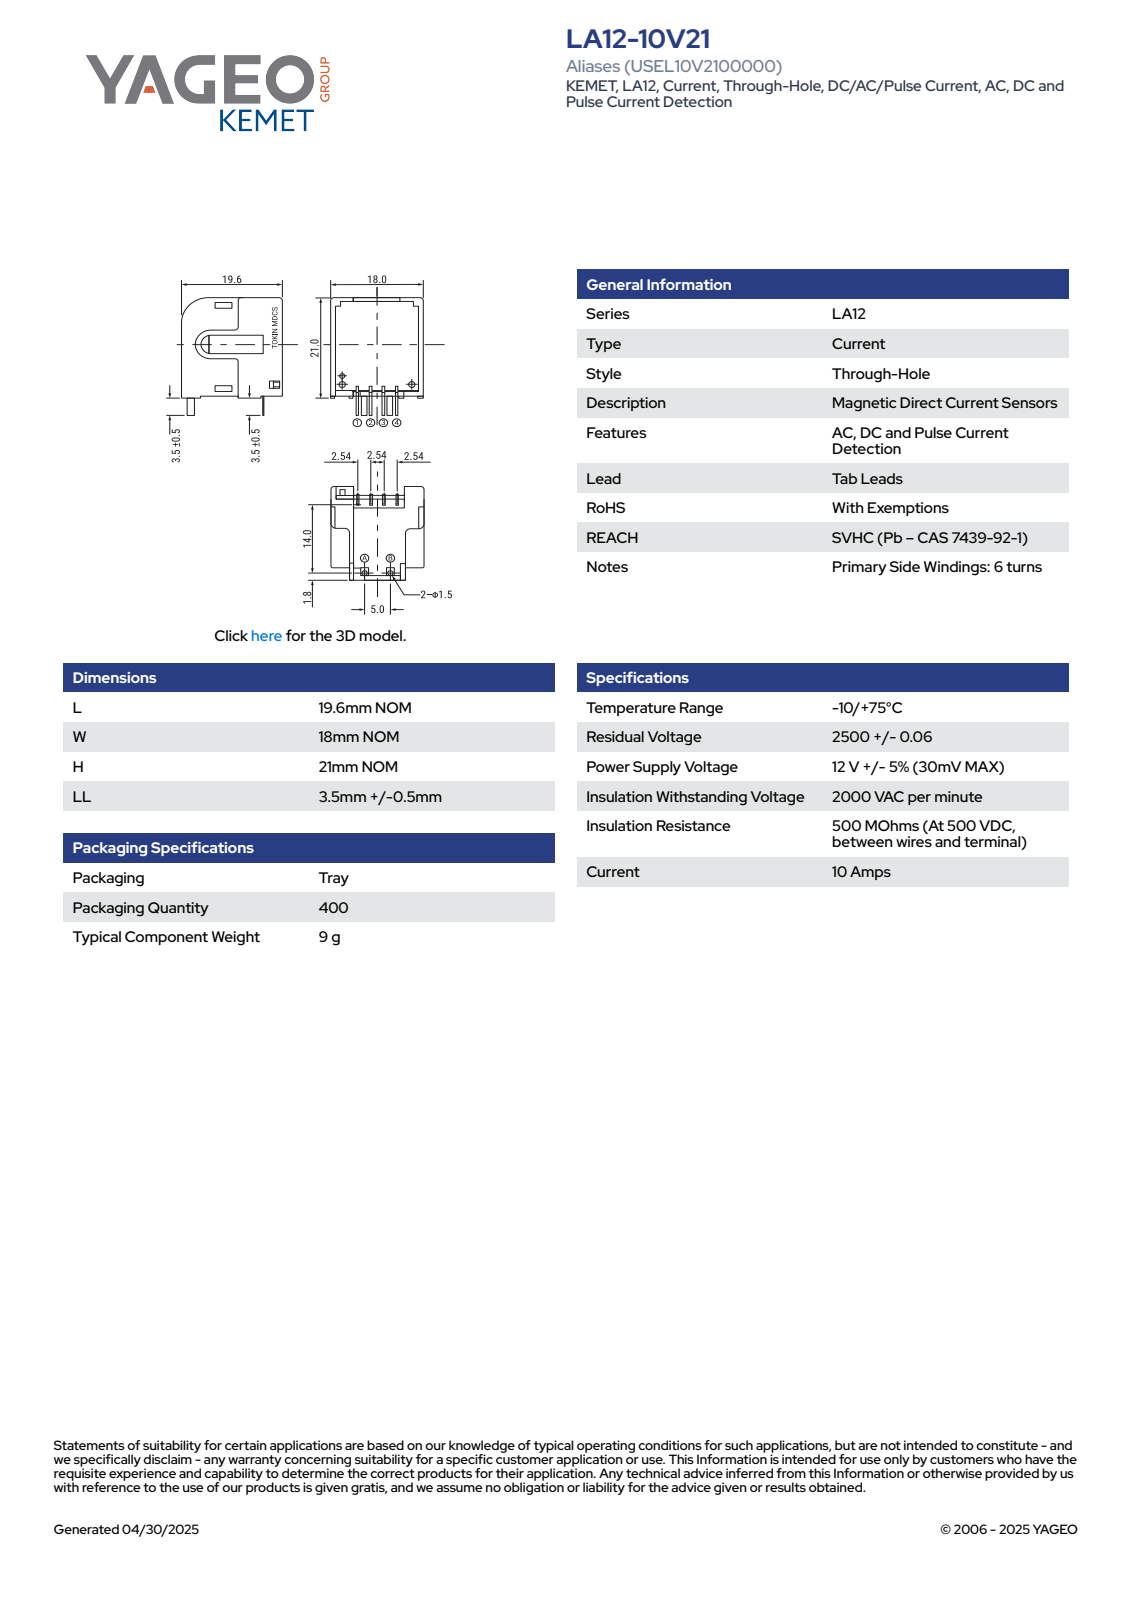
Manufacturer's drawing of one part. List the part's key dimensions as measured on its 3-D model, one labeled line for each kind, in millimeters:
Part name (STEP PRODUCT): SC_KLA1210V_L19.6W18H21LL4
STEP written by: SolidWorks 2014 (AUTOMOTIVE_DESIGN)
Units: millimetres
Bodies: 1 solid, 150 faces (110 planar, 31 cylindrical, 9 other)
Overall size (bounding box): 25 × 19.6 × 18
Volume: 4 129 mm³ · Surface area: 3 109 mm²
Round bosses / shafts (diameter × count): ⌀1.5 ×2, ⌀5 ×1
Partial cylindrical surfaces — rounded edges, fillets, slot ends (radius × count): R0.3 ×12, R0.5 ×3, R5 ×1
Main face-to-face distances: 4, 14, 18, 4.7, 13.3, 0.7, 9.3, 10, 3.8, 3.7
